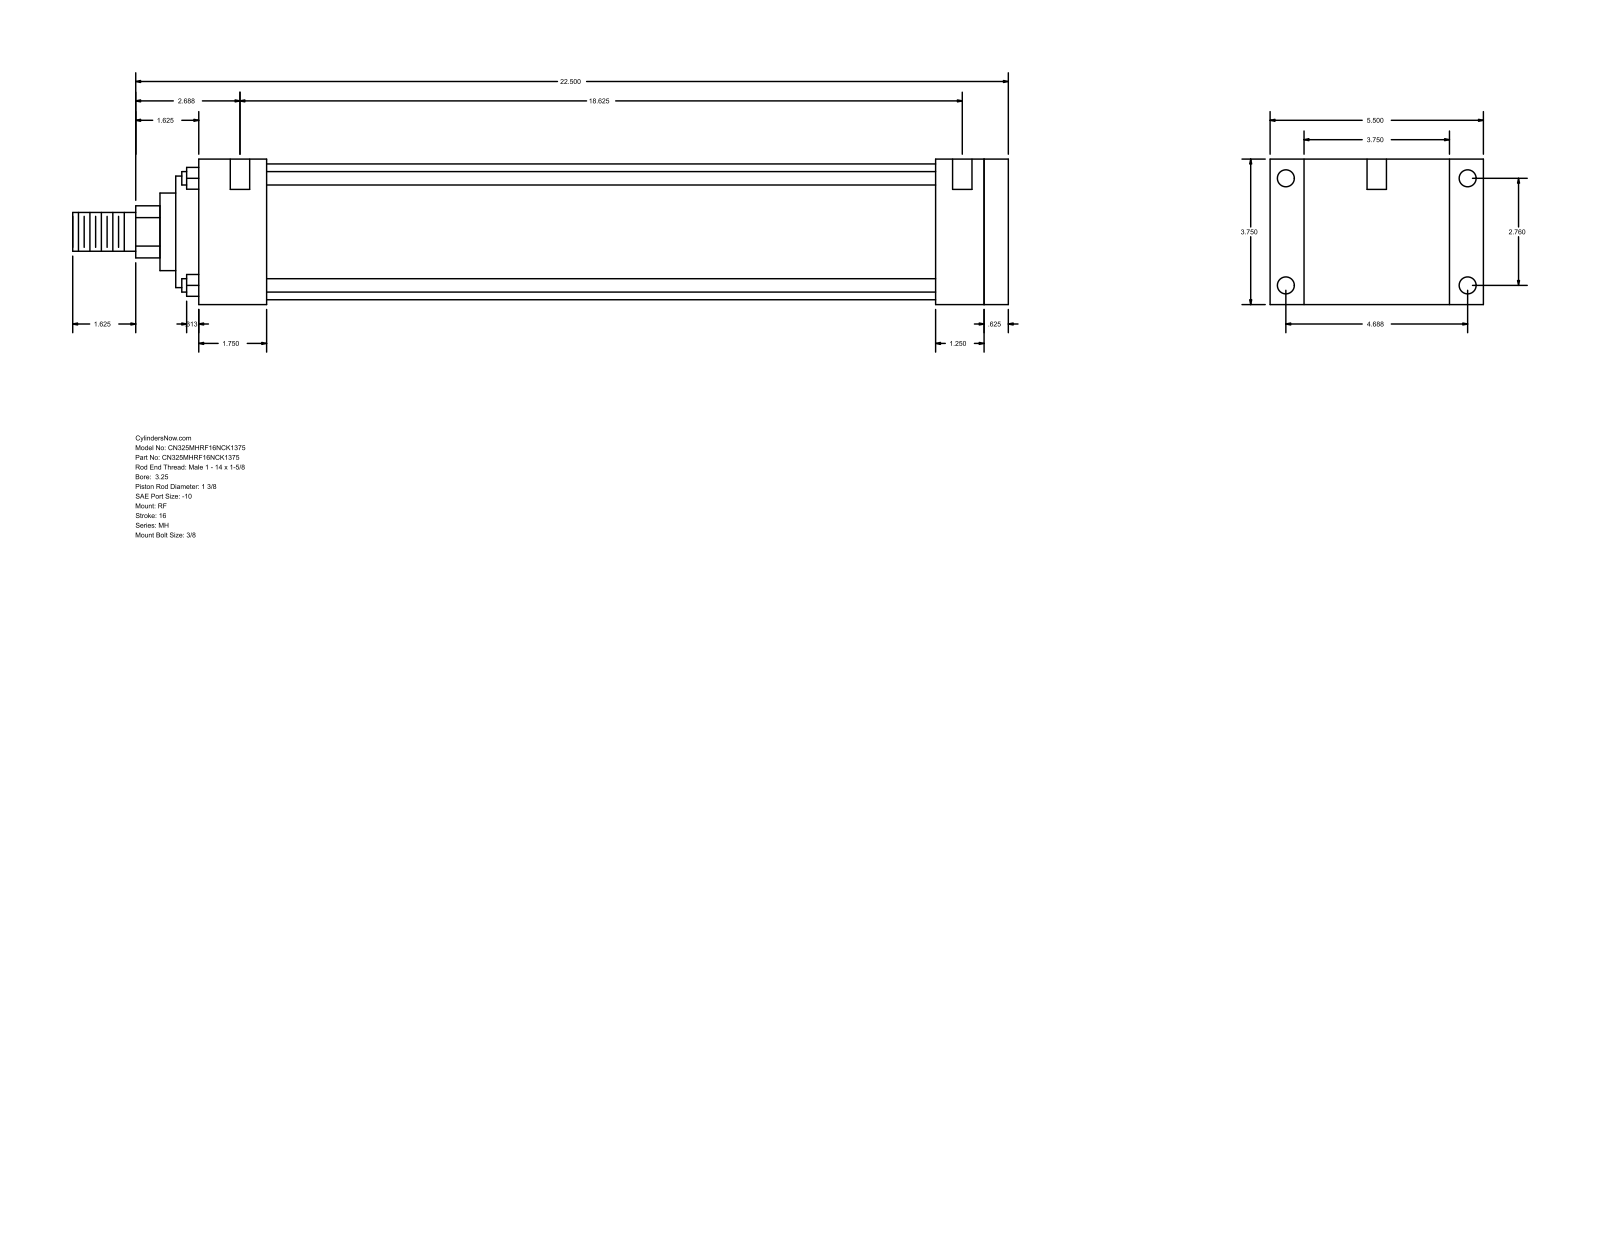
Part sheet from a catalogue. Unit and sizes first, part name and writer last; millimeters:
Units: millimetres
Overall size (bounding box): 612.77 × 139.7 × 95.25
Round holes (diameter × count): ⌀5.56 ×4, ⌀11.13 ×4, ⌀12.7 ×2
Round bosses / shafts (diameter × count): ⌀8.76 ×4, ⌀88.9 ×1, ⌀73.03 ×1, ⌀50.8 ×1, ⌀34.92 ×1, ⌀25.4 ×1
Partial cylindrical surfaces — rounded edges, fillets, slot ends (radius × count): R17.06 ×1
Main face-to-face distances: 95.24, 530.23, 15.88, 514.35, 22.23, 117.47, 44.45, 469.9, 485.78, 482.61
Hole centre spacings: 70.1, 119.06, 138.16, 479.43, 1.59, 4.76, 473.08, 474.67
Bodies: 0 solids, 94 faces (65 planar, 29 cylindrical, 0 other)
Part name (STEP PRODUCT): MH_RF__0325_1.375
STEP written by: GSSL Pune (CONFIG_CONTROL_DESIGN)
